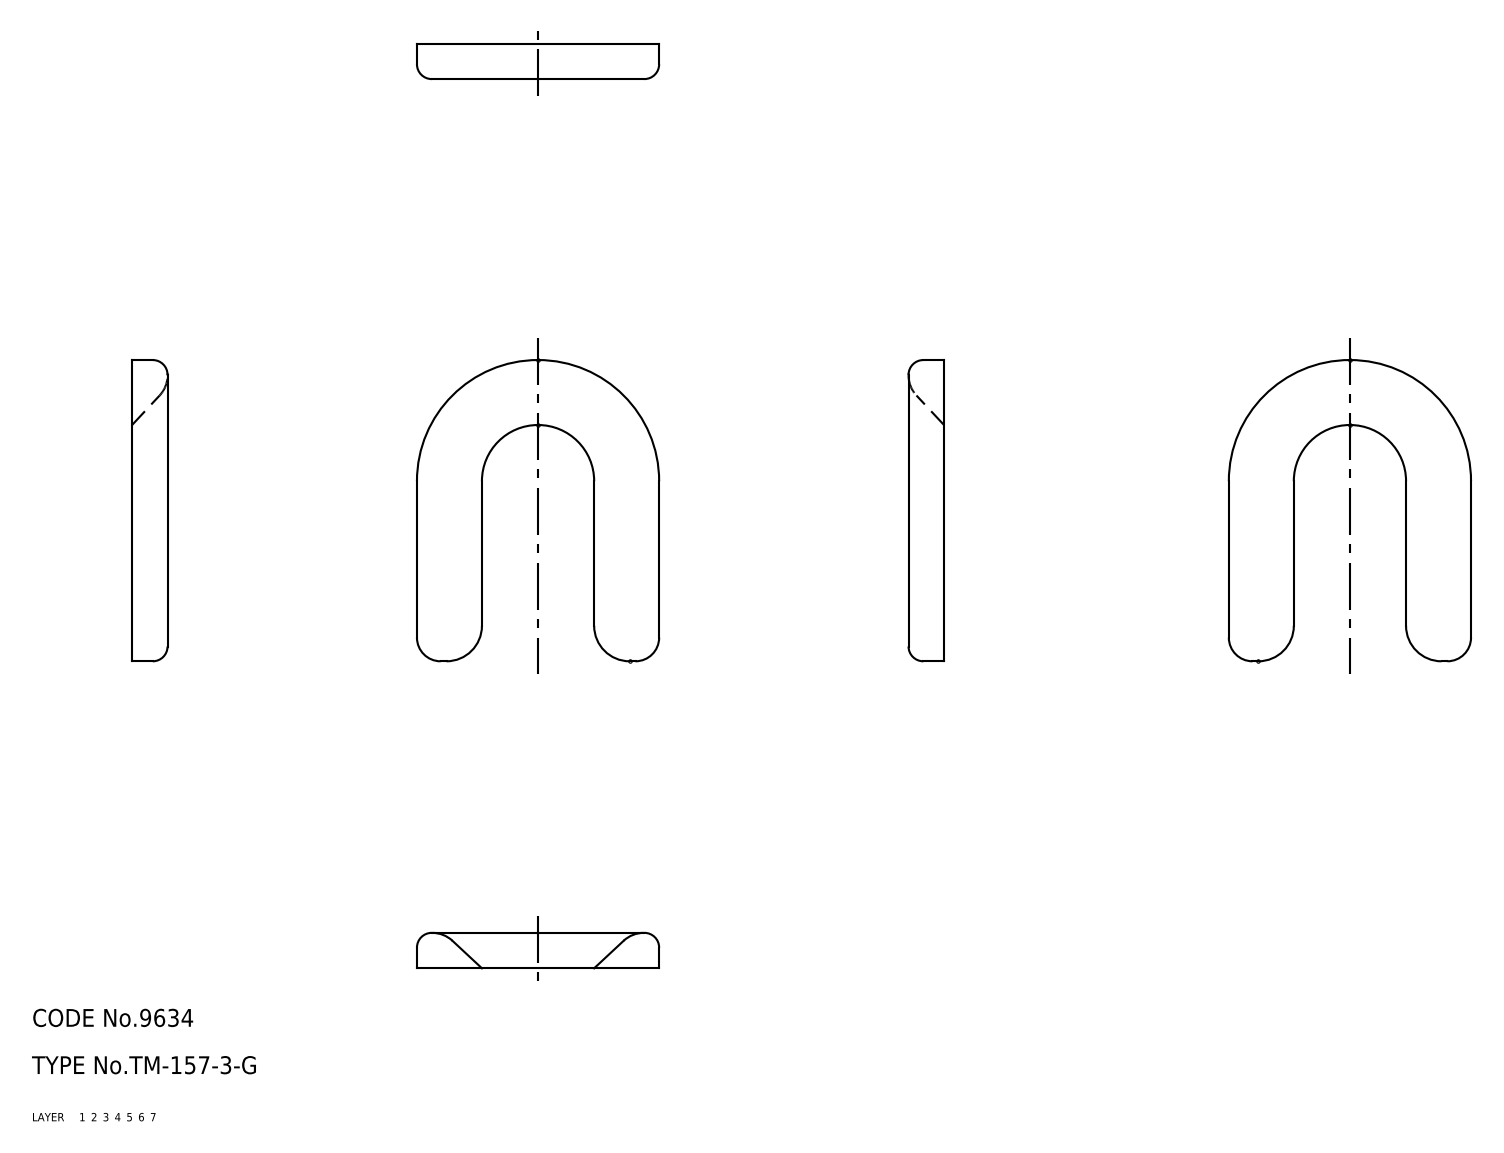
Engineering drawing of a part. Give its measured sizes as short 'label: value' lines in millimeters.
name: holder; TM_157_3_G
written by: SolidWorks 2015 (AUTOMOTIVE_DESIGN)
unit: mm
bodies: 1 solid, 34 faces (8 planar, 11 cylindrical, 15 other)
size: 51 × 41 × 6
volume: 4 955 mm³; area: 3 219 mm²
rounds: 3× R2.5, 2× R4, 2× R5, 2× R6, 1× R20.5
face distances: 41, 6
